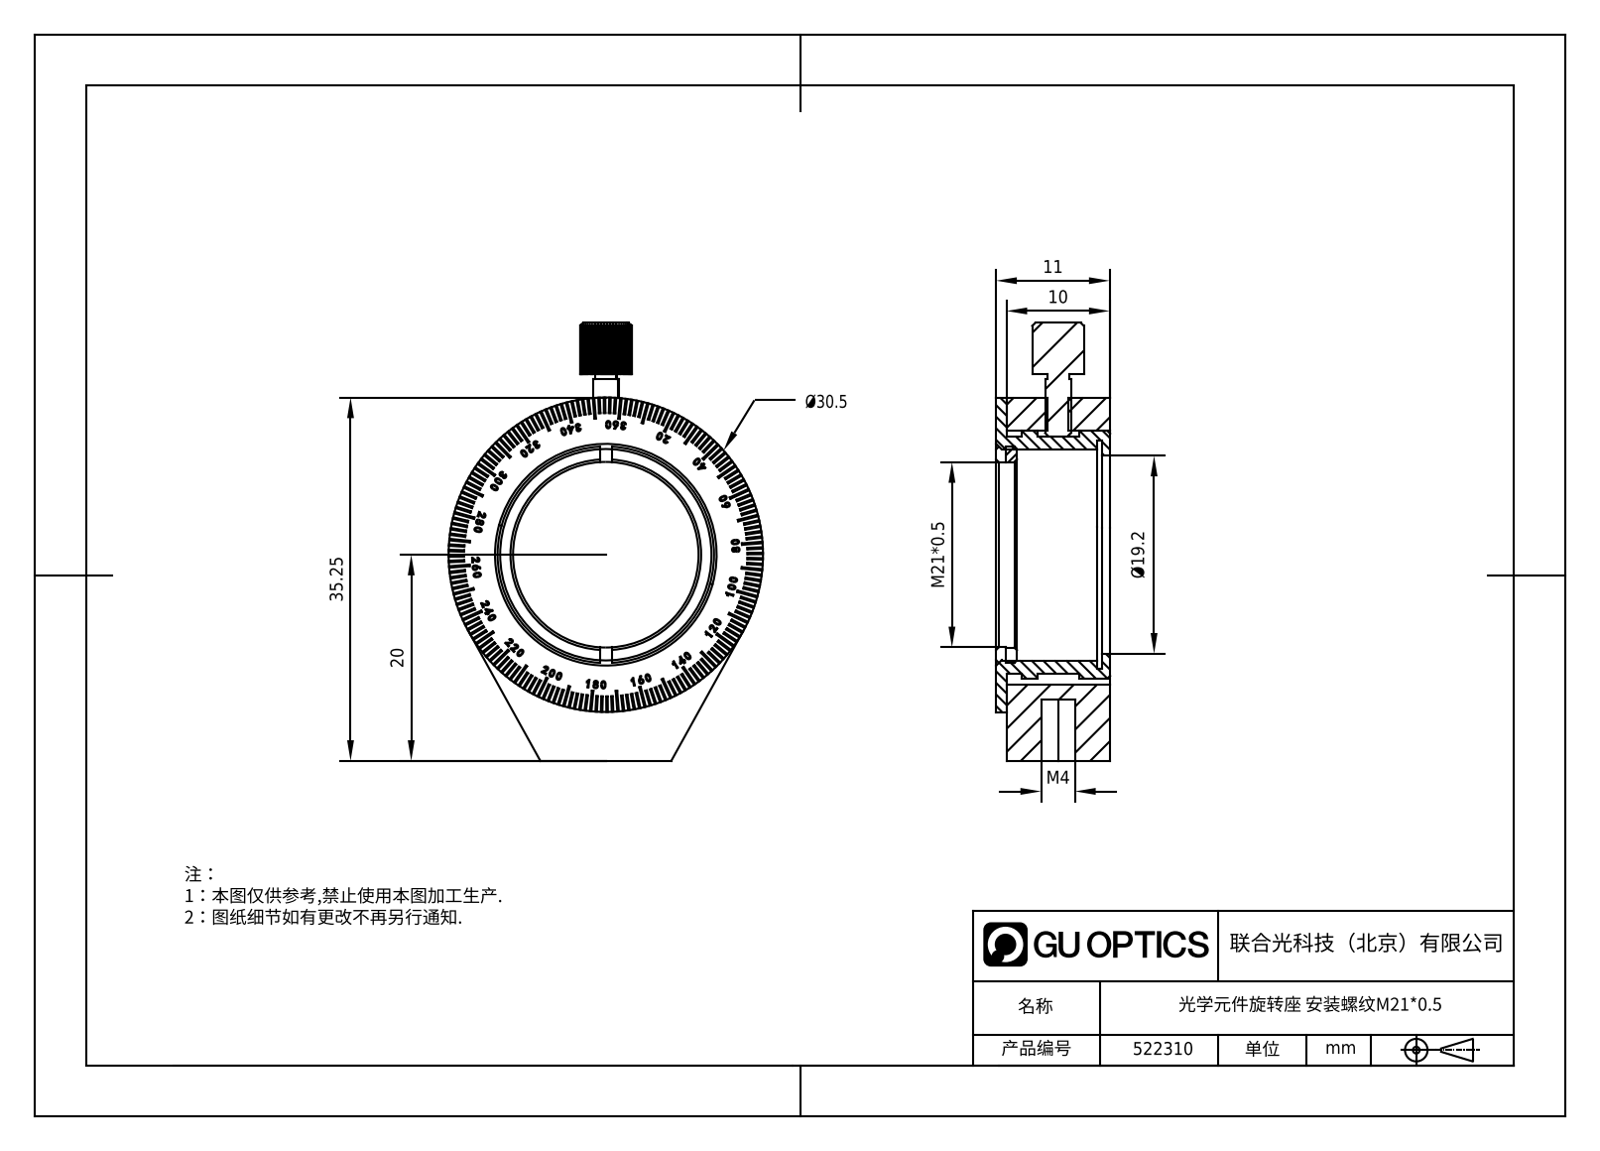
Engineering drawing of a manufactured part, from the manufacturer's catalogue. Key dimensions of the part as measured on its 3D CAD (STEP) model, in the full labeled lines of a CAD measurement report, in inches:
Part name (STEP PRODUCT): SNTY_一体式手拧旋钮_30.13.2.2.3_SNTY-M2.5x6-0511; ZFK透镜卡环压圈_1.8.5.14-ZFK-K20
STEP written by: SolidWorks 2021 (CONFIG_CONTROL_DESIGN)
Units: inches
Bodies: 4 solids, 1355 faces (1082 planar, 83 cylindrical, 190 other)
Overall size (bounding box): 1.673 × 1.201 × 0.435
Volume: 0.326 in³ · Surface area: 9.233 in²
Round holes (diameter × count): ⌀0.081 ×1, ⌀0.13 ×1, ⌀0.709 ×1, ⌀0.756 ×1, ⌀0.807 ×1, ⌀0.87 ×1
Round bosses / shafts (diameter × count): ⌀1.201 ×1, ⌀0.945 ×1, ⌀0.906 ×1, ⌀0.827 ×1, ⌀0.098 ×1, ⌀0.083 ×1
Partial cylindrical surfaces — rounded edges, fillets, slot ends (radius × count): R0.098 ×1, R0.426 ×1
Main face-to-face distances: 0.039, 0.433, 0.394, 0.396, 0.435, 0.031, 0.03, 0.364, 0.404, 0.02
